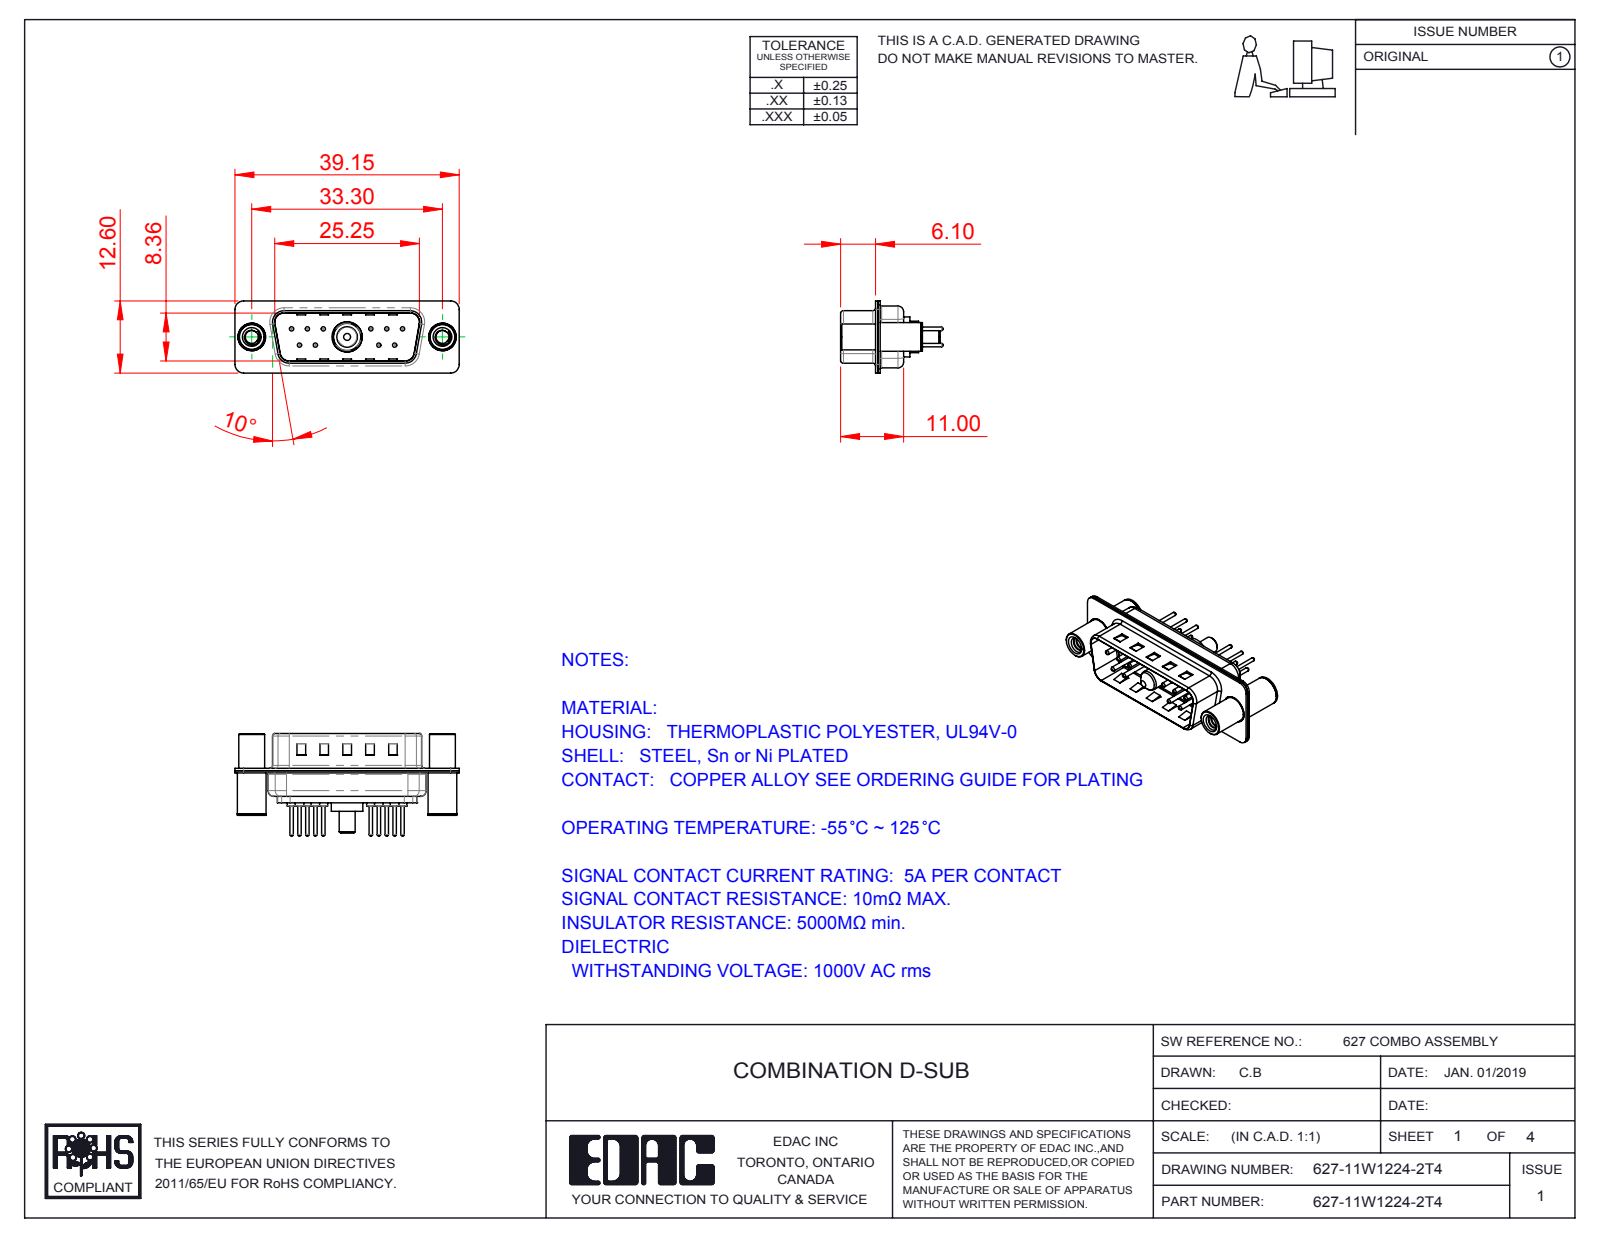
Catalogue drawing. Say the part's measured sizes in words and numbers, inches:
The part is named "627Combo Contact Row 2_24; Power Pin_20A S; 627-11W1224-2T4; 627Combo Shell Front_15 Contacts (+4 more)". Its 3-D file was written by "SolidWorks 2016 (CONFIG_CONTROL_DESIGN)". It is 17 solids with 849 faces: 234 planar, 348 cylindrical and 267 other. Overall it measures 1.541 by 0.705 by 0.496 inches. Its volume is 0.134 cubic inches and its surface area 8.244 square inches. Round holes: 10 of diameter 0.03, 10 of diameter 0.063, 10 of diameter 0.079, 2 of diameter 0.089, 2 of diameter 0.128, 2 of diameter 0.157, 2 of diameter 0.189, 1 of diameter 0.191, 1 of diameter 0.209. Round bosses or shafts: 10 of diameter 0.059, 10 of diameter 0.024, 2 of diameter 0.197, 2 of diameter 0.193, 2 of diameter 0.177, 1 of diameter 0.217, 1 of diameter 0.205, 1 of diameter 0.187. Partial cylindrical surfaces (rounded edges, fillets, slot ends): 20 of radius 0.059, 12 of radius 0.079, 8 of radius 0.02, 8 of radius 0.063, 7 of radius 0.039, 4 of radius 0.01, 4 of radius 0.024, 4 of radius 0.026. The main face-to-face distances are 0.016, 0.032, 0.377, 0.345, 0.031, 0.059, 0.22, 0.236, 0.205, 0.048. The hole center spacings are 0.124, 0.109, 0.545, 0.436, 0.654, 0.198, 0.198, 0.218.
